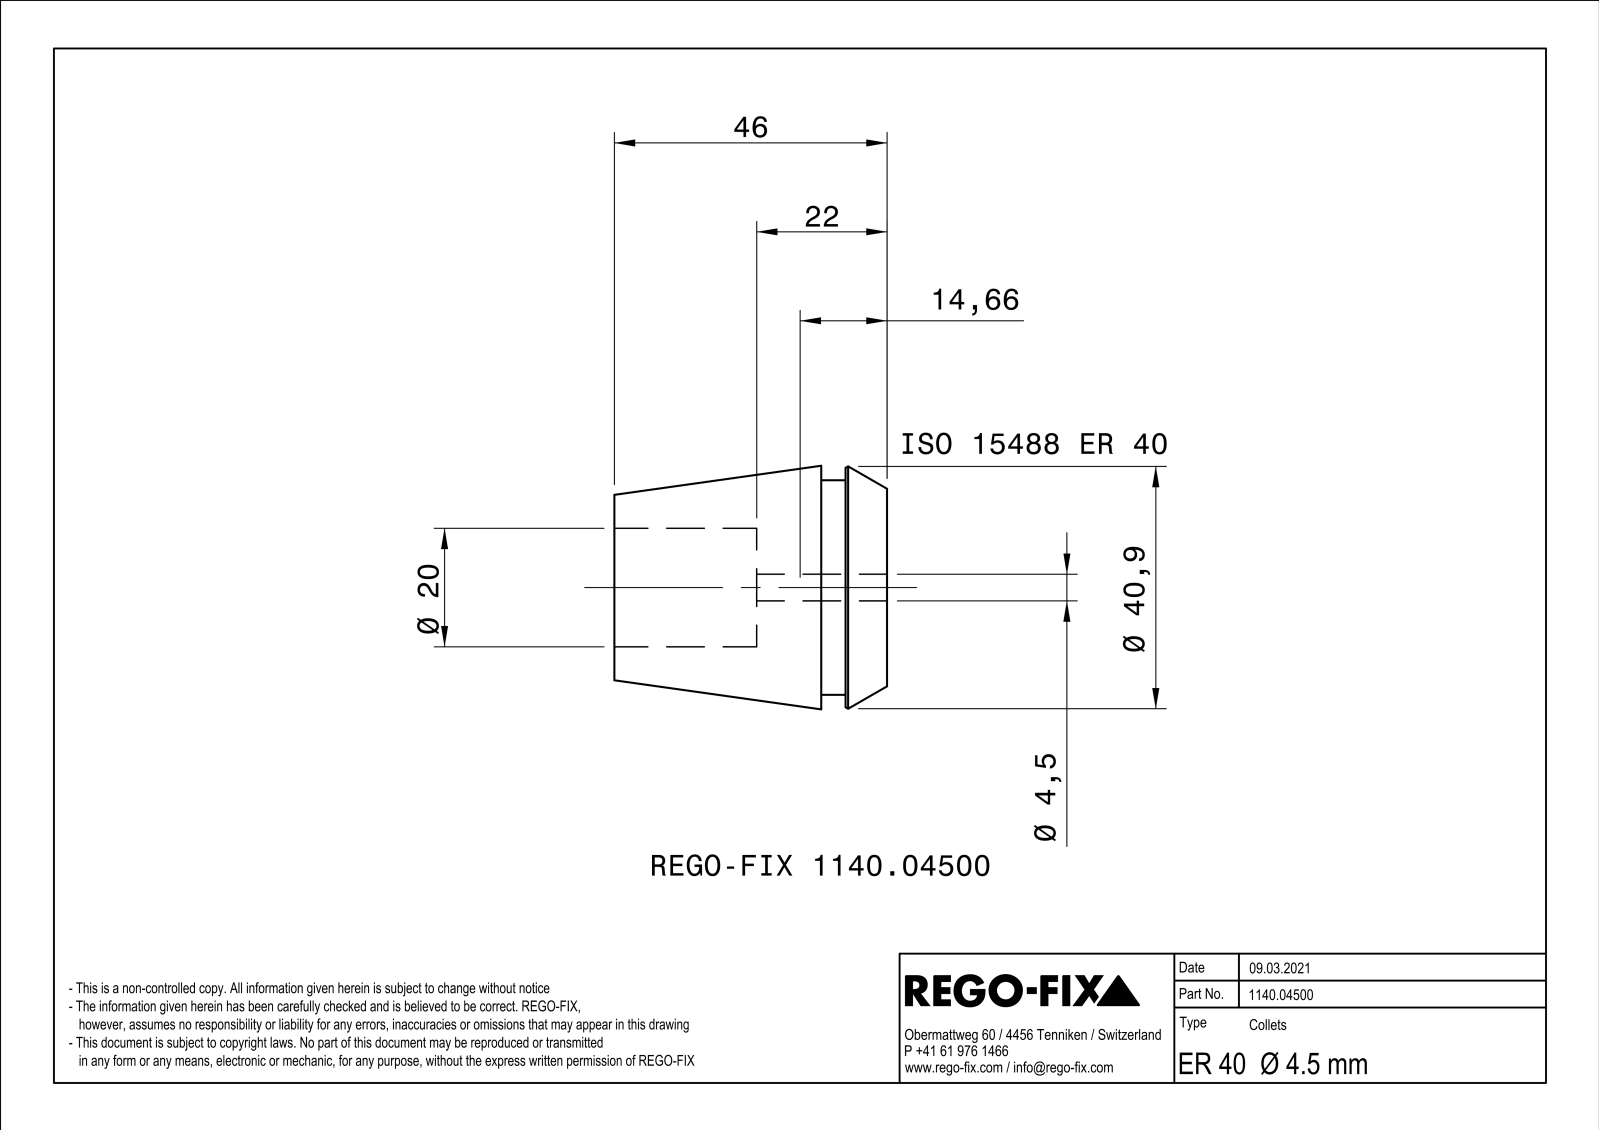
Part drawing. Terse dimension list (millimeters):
name: NOCUT
written by: SIEMENS PLM Software Solid Edge ST10 (AUTOMOTIVE_DESIGN)
unit: mm
bodies: 1 solid, 272 faces (104 planar, 48 cylindrical, 120 other)
size: 46 × 41.09 × 41.09
volume: 34 927 mm³; area: 21 239 mm²
holes: 1× ⌀20
bosses: 1× ⌀36.2
rounds: 8× R45, 1× R2.25
face distances: 0.8, 0.78, 0.82, 46, 11.1, 34.9, 7, 4.1, 39, 22
